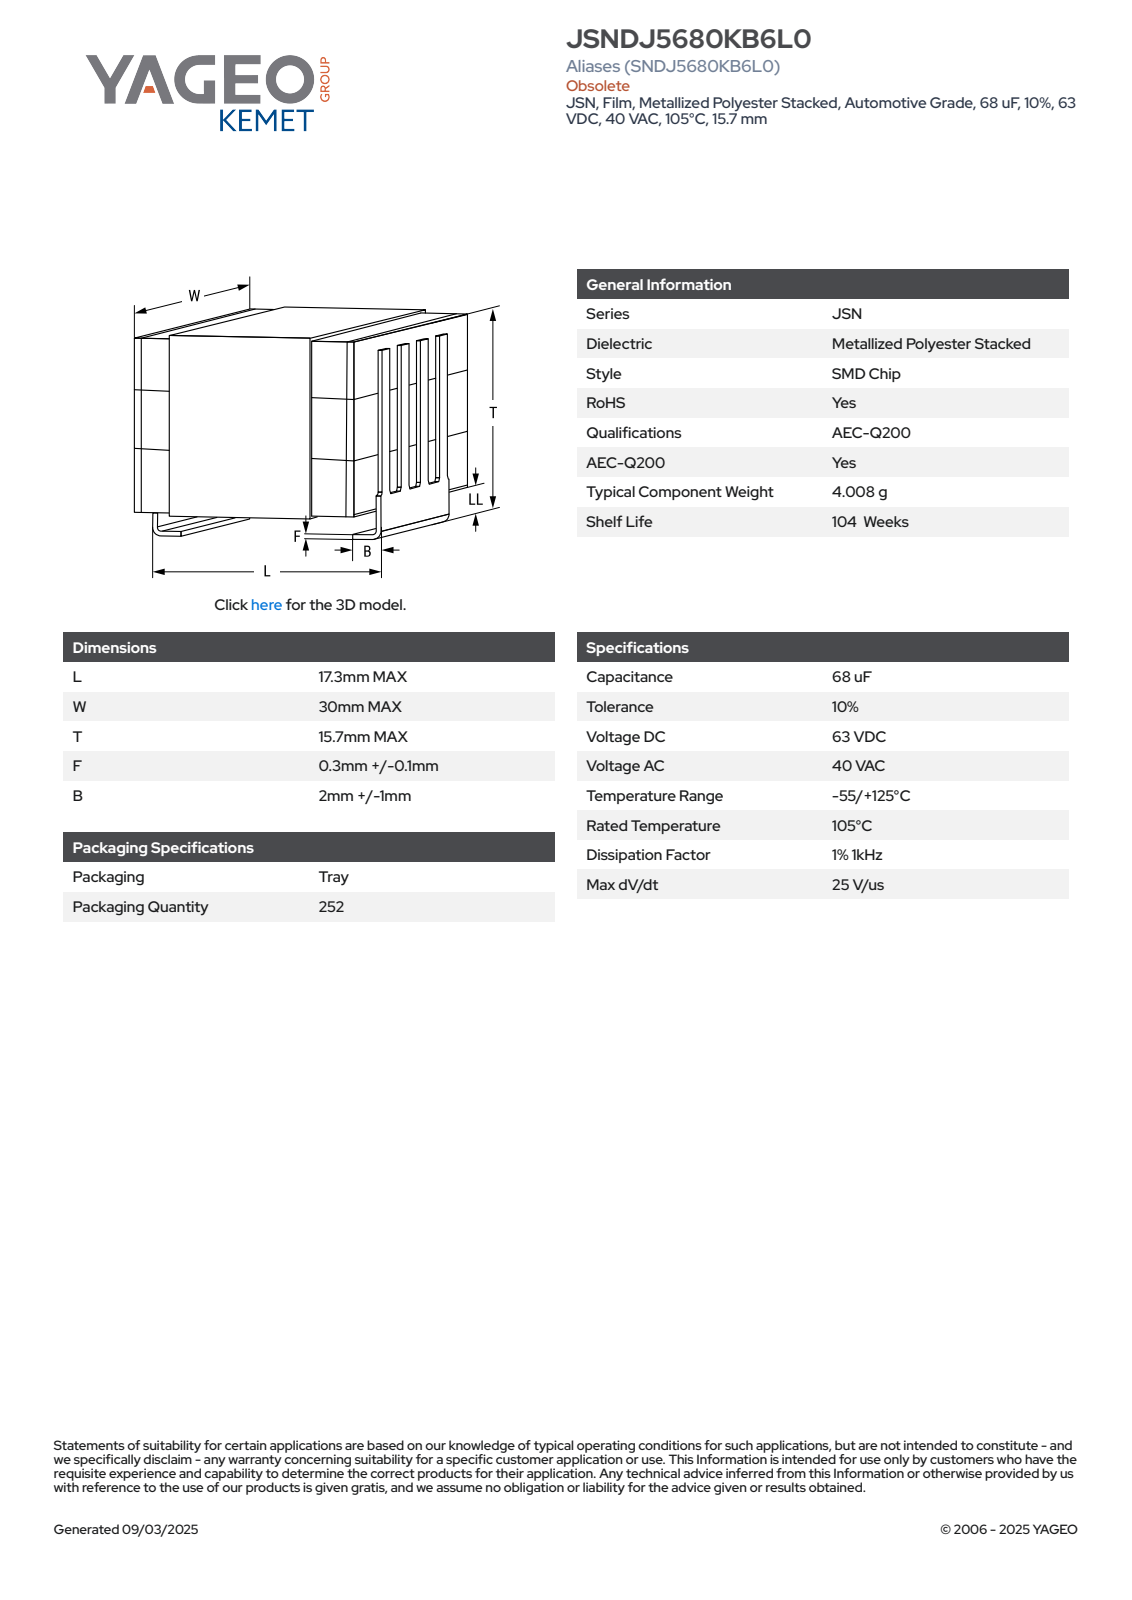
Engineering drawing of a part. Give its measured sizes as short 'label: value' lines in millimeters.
name: CFS_KJSN_L17.3W30T15.7F0.40
written by: SolidWorks 2014 (AUTOMOTIVE_DESIGN)
unit: mm
bodies: 4 solids, 101 faces (97 planar, 4 cylindrical, 0 other)
size: 30 × 17.3 × 15.7
volume: 6 393 mm³; area: 3 915 mm²
rounds: 4× R0.2
face distances: 4.18, 8.42, 8.32, 4.08, 4.24, 0.4, 16.9, 4.28, 8.52, 12.6
